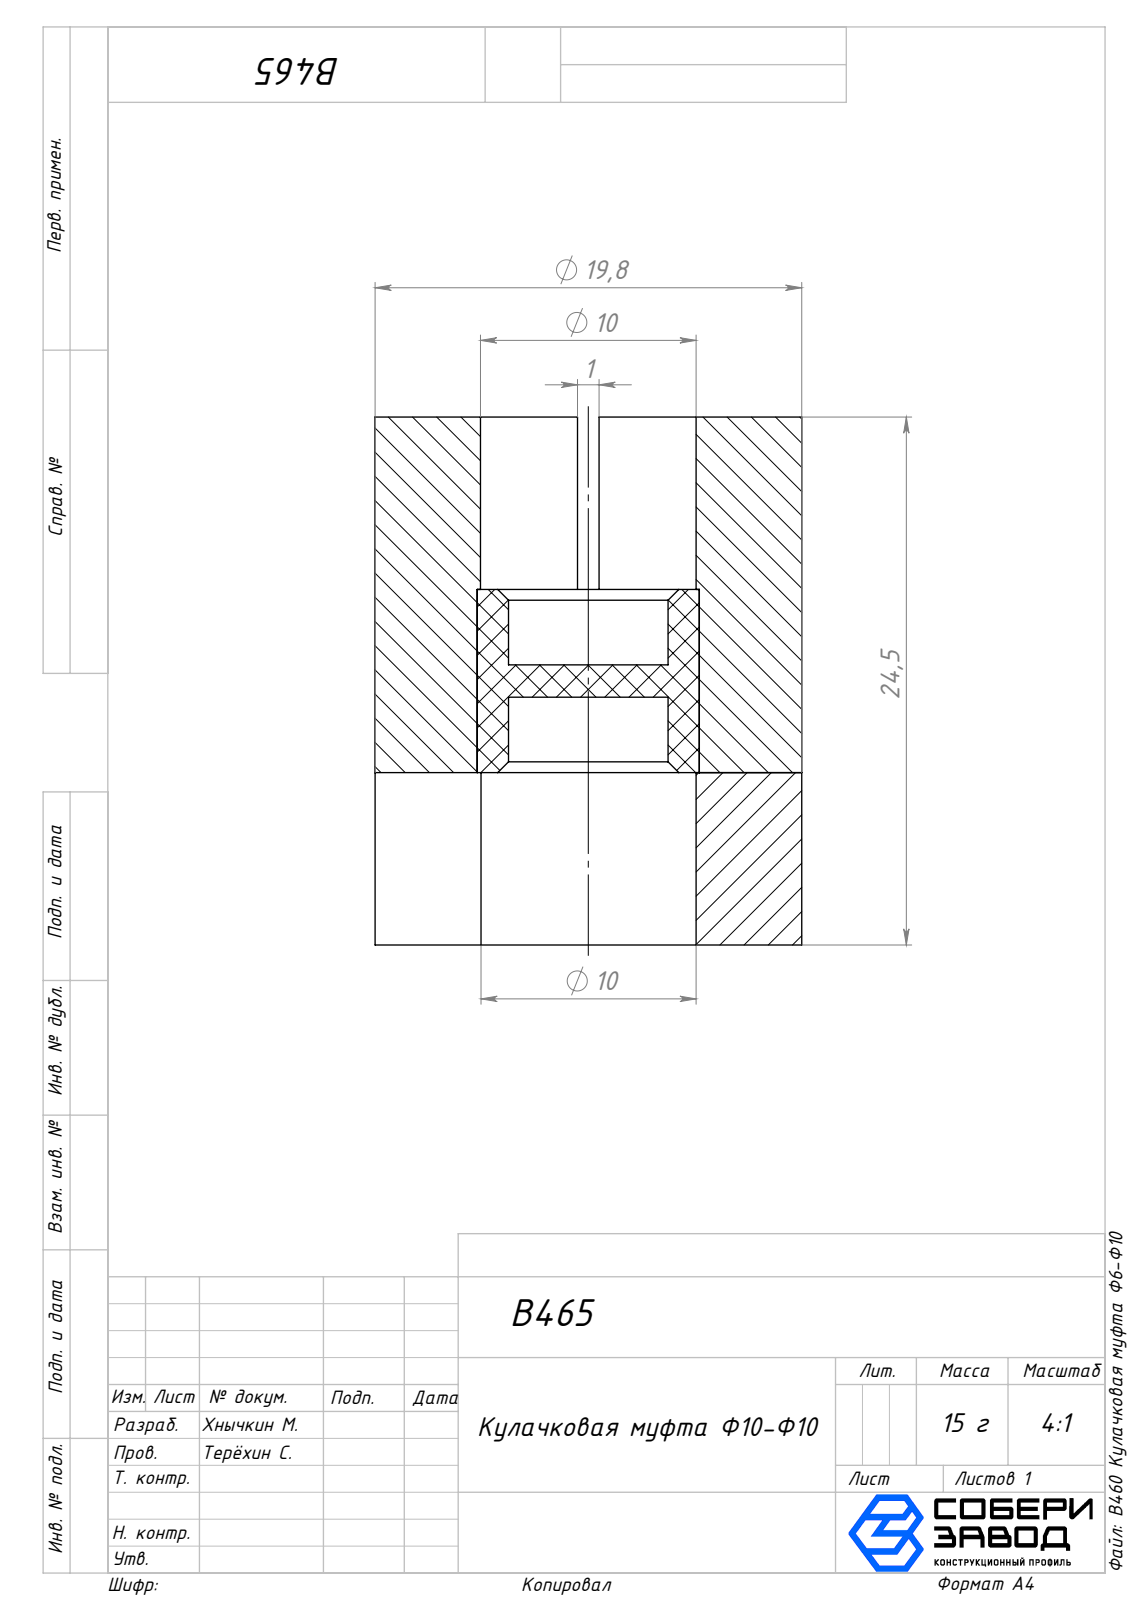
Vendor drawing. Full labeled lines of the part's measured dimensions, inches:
Part name (STEP PRODUCT): Верх_00; Середина_00; Низ_00; B465 Кулачковая муфта Ф10-Ф10
STEP written by: SolidWorks 2025 (AUTOMOTIVE_DESIGN)
Units: inches
Bodies: 3 solids, 56 faces (24 planar, 28 cylindrical, 4 other)
Overall size (bounding box): 0.965 × 0.78 × 0.78
Volume: 0.36 in³ · Surface area: 6.939 in²
Round holes (diameter × count): ⌀0.291 ×1, ⌀0.394 ×1
Round bosses / shafts (diameter × count): ⌀0.78 ×1
Partial cylindrical surfaces — rounded edges, fillets, slot ends (radius × count): R0.236 ×8
Main face-to-face distances: 0.315, 0.65, 0.335, 0.965, 0.183, 0.222, 0.453, 0.512, 0.138, 0.197
